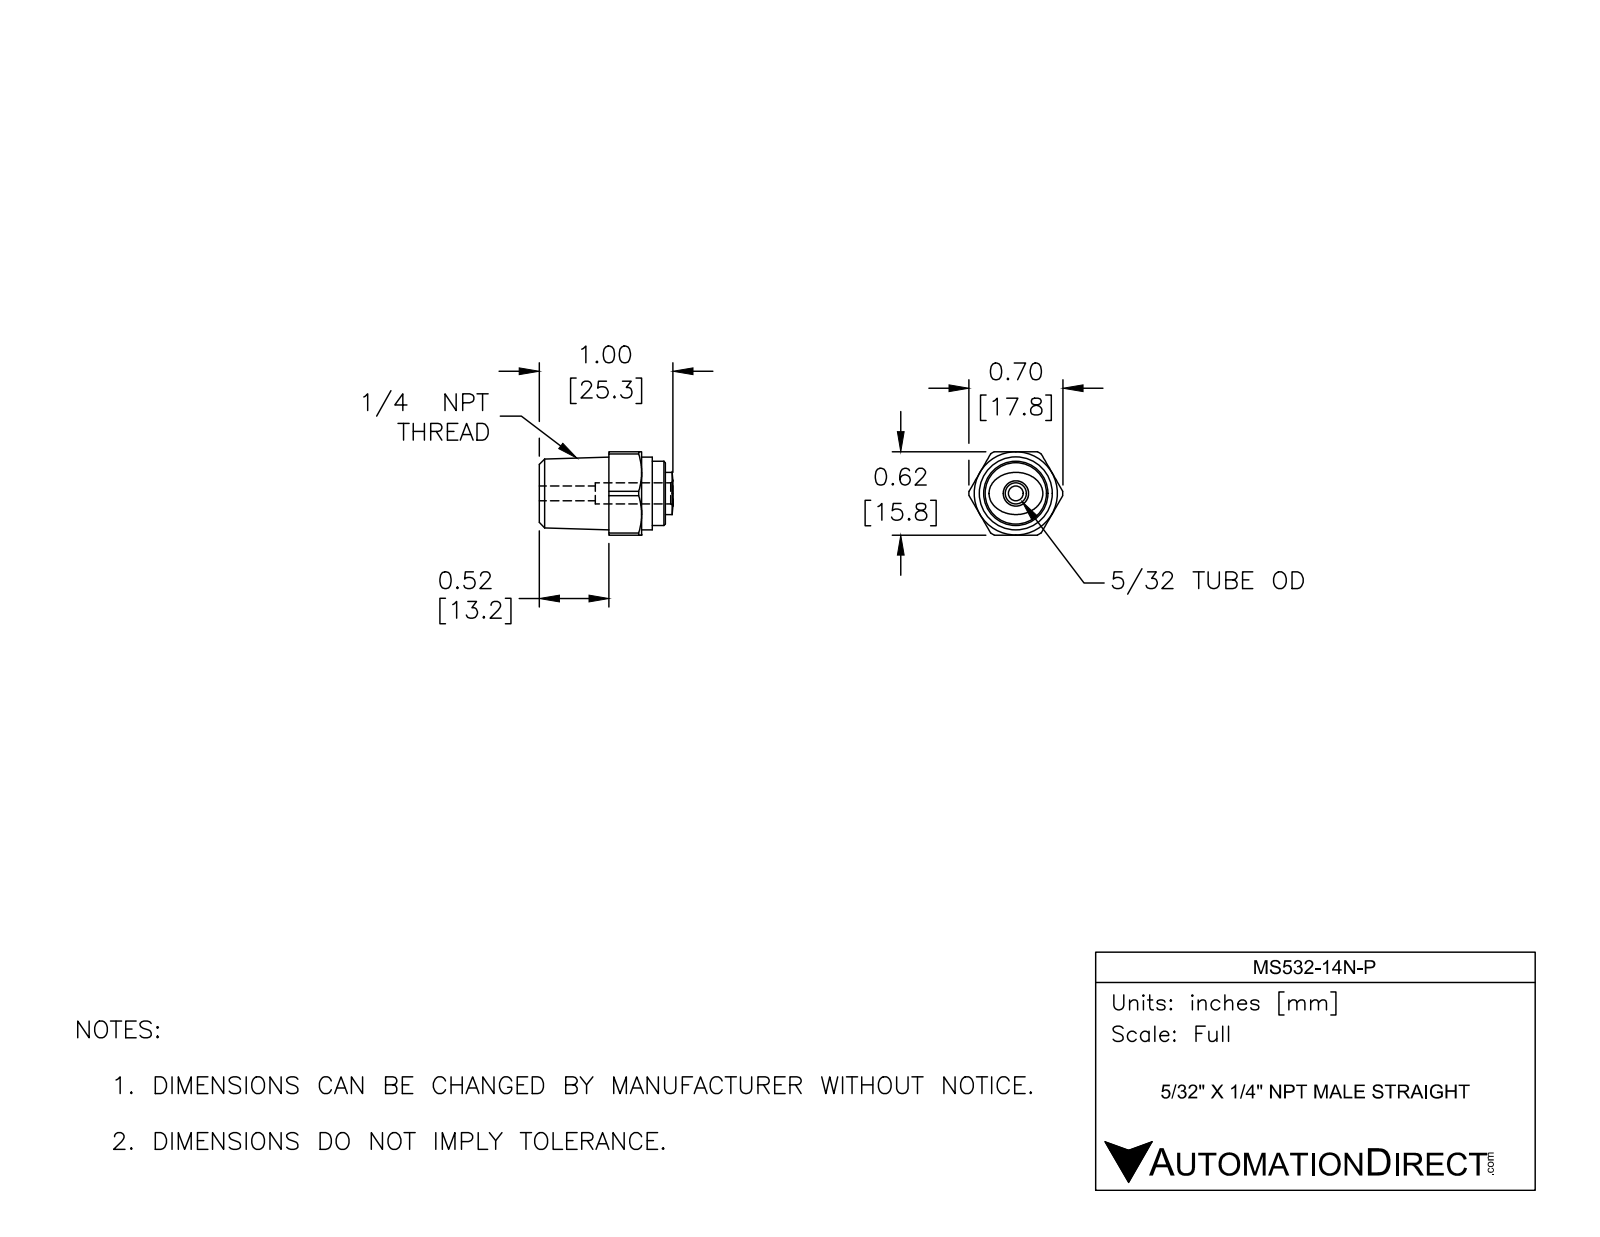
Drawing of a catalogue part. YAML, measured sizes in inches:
part_name: "MS532-14N-P"
step_written_by: "SolidWorks 2017 (AUTOMOTIVE_DESIGN)"
units: inches
bodies: {solids: 1, faces: 44, planar: 12, cylindrical: 14, other: 18}
overall_size: [0.996, 0.701, 0.622]
volume: 0.22
surface_area: 2.706
round_holes:
  - {diameter: 0.11, count: 1}
  - {diameter: 0.157, count: 1}
round_bosses_or_shafts:
  - {diameter: 0.543, count: 1}
  - {diameter: 0.48, count: 1}
partial_cylinders:
  - {radius: 0.35, count: 1}
face_to_face_distances: [0.622, 0.52, 0.764, 0.244, 0.941, 0.421, 0.177, 0.843, 0.323, 0.079]
